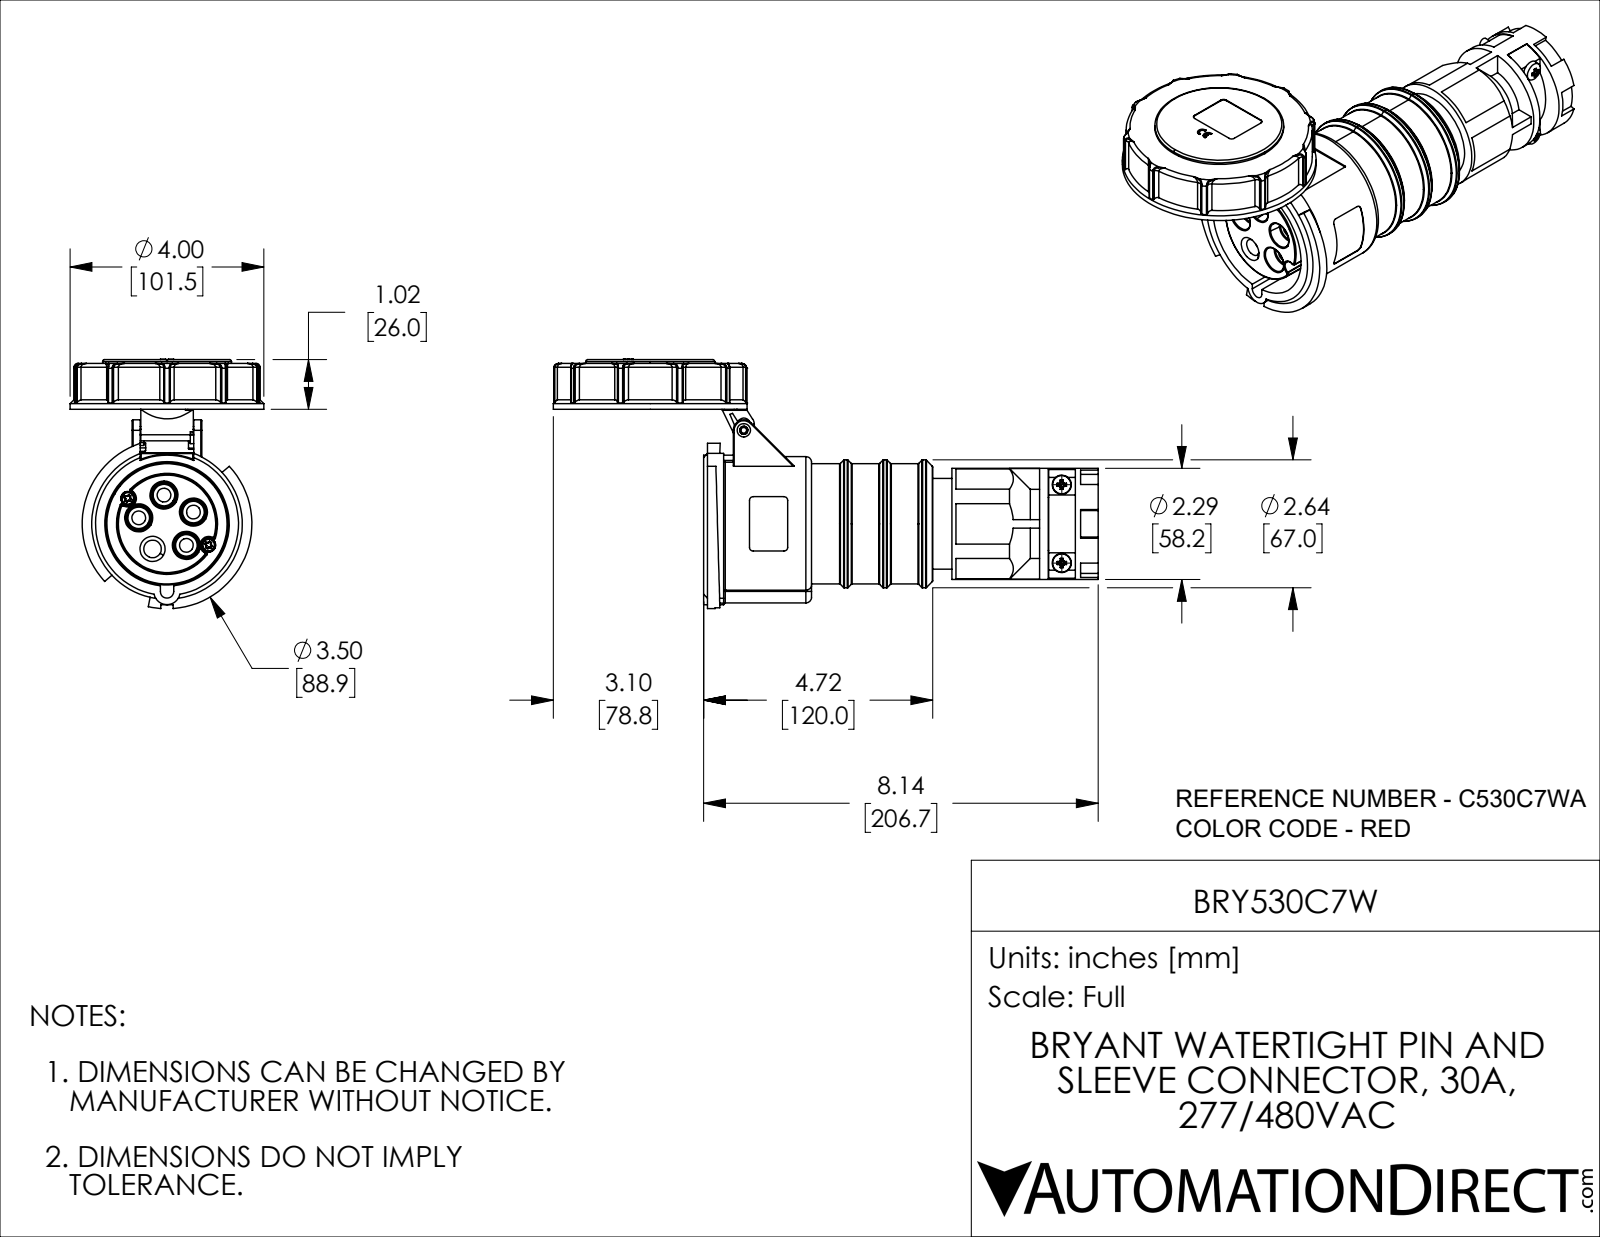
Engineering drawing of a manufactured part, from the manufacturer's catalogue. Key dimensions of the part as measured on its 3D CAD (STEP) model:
Part name (STEP PRODUCT): BRY530C7W
STEP written by: SolidWorks 2021 (CONFIG_CONTROL_DESIGN)
Units: millimetres
Bodies: 7 solids, 946 faces (312 planar, 312 cylindrical, 322 other)
Overall size (bounding box): 285.45 × 130.83 × 101.5
Volume: 679 311 mm³ · Surface area: 128 186 mm²
Round holes (diameter × count): ⌀7.2 ×4, ⌀5 ×2, ⌀3 ×1, ⌀4.3 ×1, ⌀7 ×1, ⌀9.2 ×1, ⌀29.5 ×1, ⌀49.04 ×1, ⌀65.2 ×1, ⌀91.5 ×1
Round bosses / shafts (diameter × count): ⌀101.5 ×1, ⌀78.9 ×1, ⌀70.4 ×1, ⌀67.5 ×1, ⌀67 ×1, ⌀64 ×1, ⌀63 ×1, ⌀58.2 ×1
Partial cylindrical surfaces — rounded edges, fillets, slot ends (radius × count): R0.5 ×33, R2.5 ×26, R2 ×8, R1 ×5, R1.25 ×4, R1.75 ×2, R3 ×2, R3.4 ×2
Main face-to-face distances: 2, 21, 4.5, 64.7, 10, 23, 18.7, 46, 127.5, 54.2
Hole centre spacings: 15.15, 17.81, 28.82, 17.82, 28.81, 41, 169.02, 180.52
